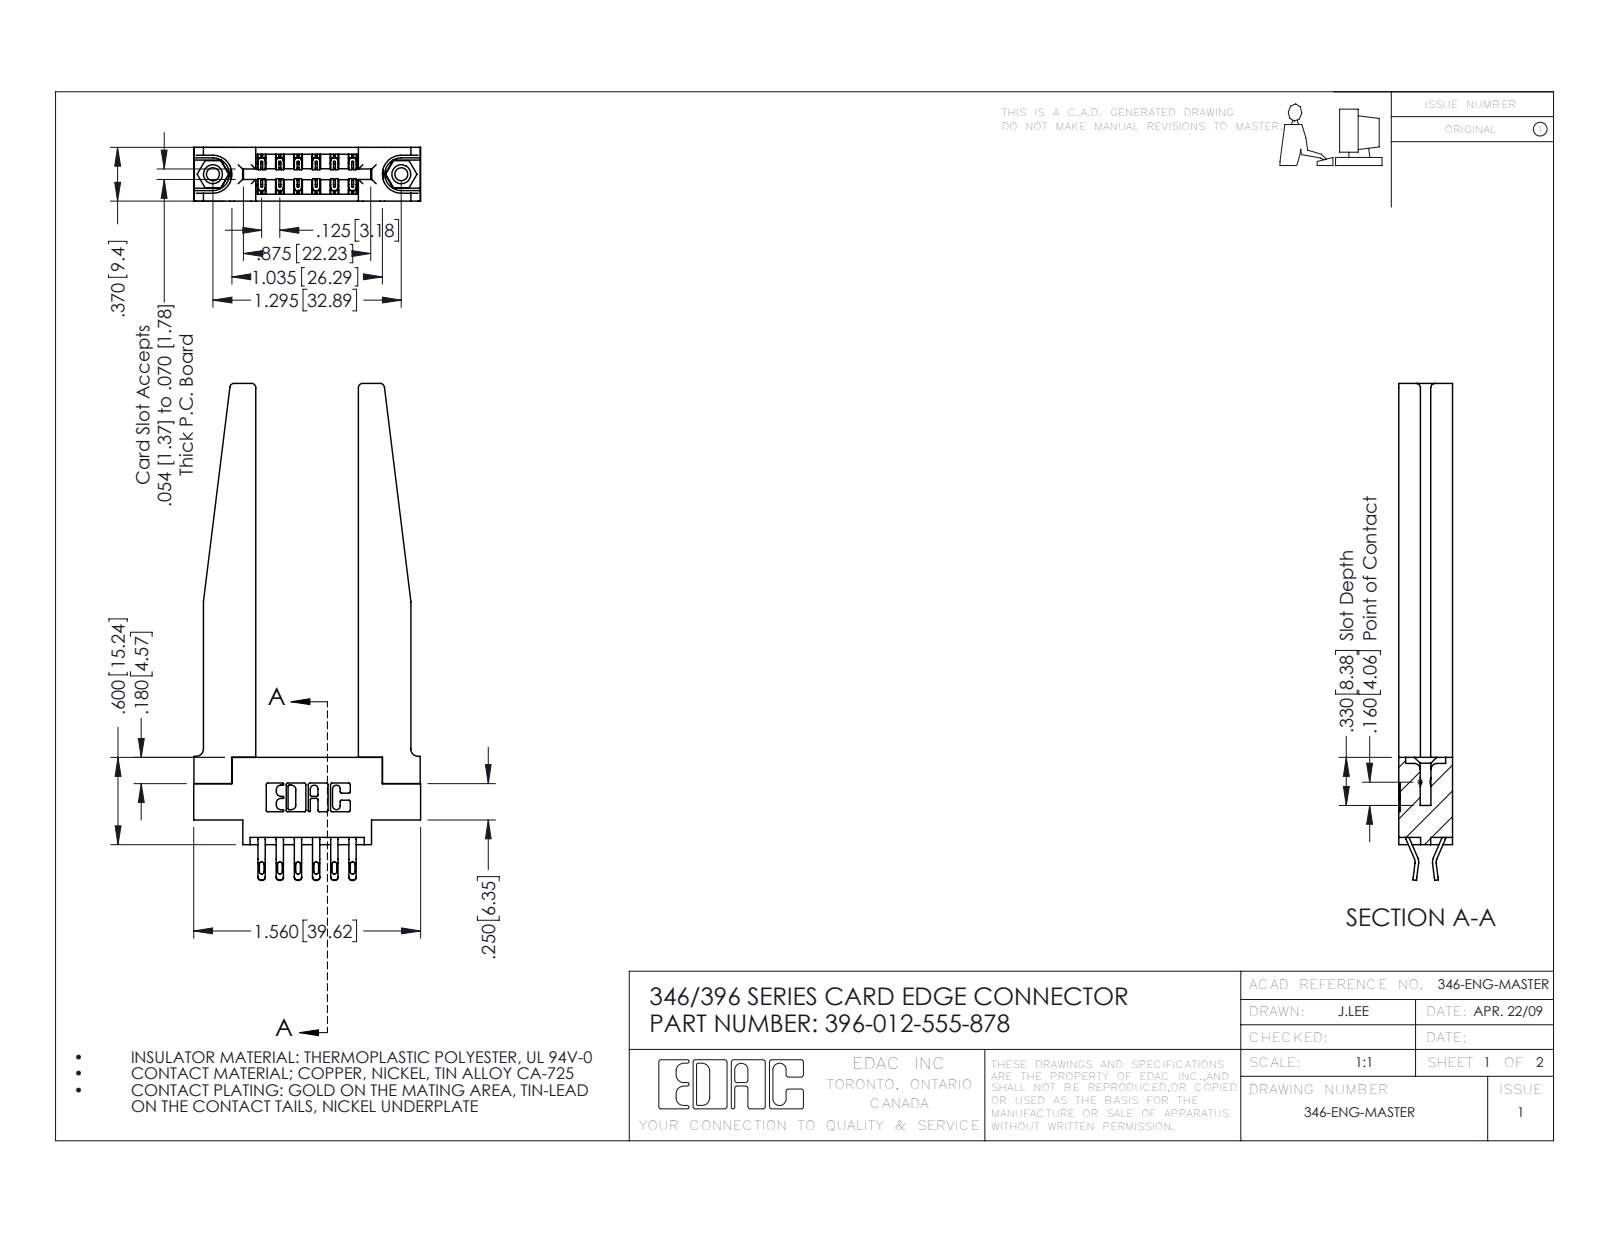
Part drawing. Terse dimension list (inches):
name: 346-220-078_345-220-078; 396-012-555-878; 345-292-001_555 Tail; 346 Part_0.170 Offset - 0.156 Dia-TH (+1 more)
written by: SolidWorks 2016 (CONFIG_CONTROL_DESIGN)
unit: in
bodies: 17 solids, 1056 faces (618 planar, 386 cylindrical, 52 other)
size: 3.415 × 1.56 × 0.37
volume: 0.633 in³; area: 17.11 in²
holes: 2× ⌀0.089, 2× ⌀0.125, 2× ⌀0.156, 1× ⌀0.064
bosses: 2× ⌀0.155
rounds: 24× R0.016, 24× R0.02, 22× R0.01, 18× R0.006, 8× R0.03, 6× R0.007, 6× R0.031, 4× R0.05
face distances: 0.37, 0.15, 0.22, 0.25, 0.706, 0.072, 0.148, 0.102, 0.048, 0.322
hole spacings: 0.246, 1.092, 1.295
